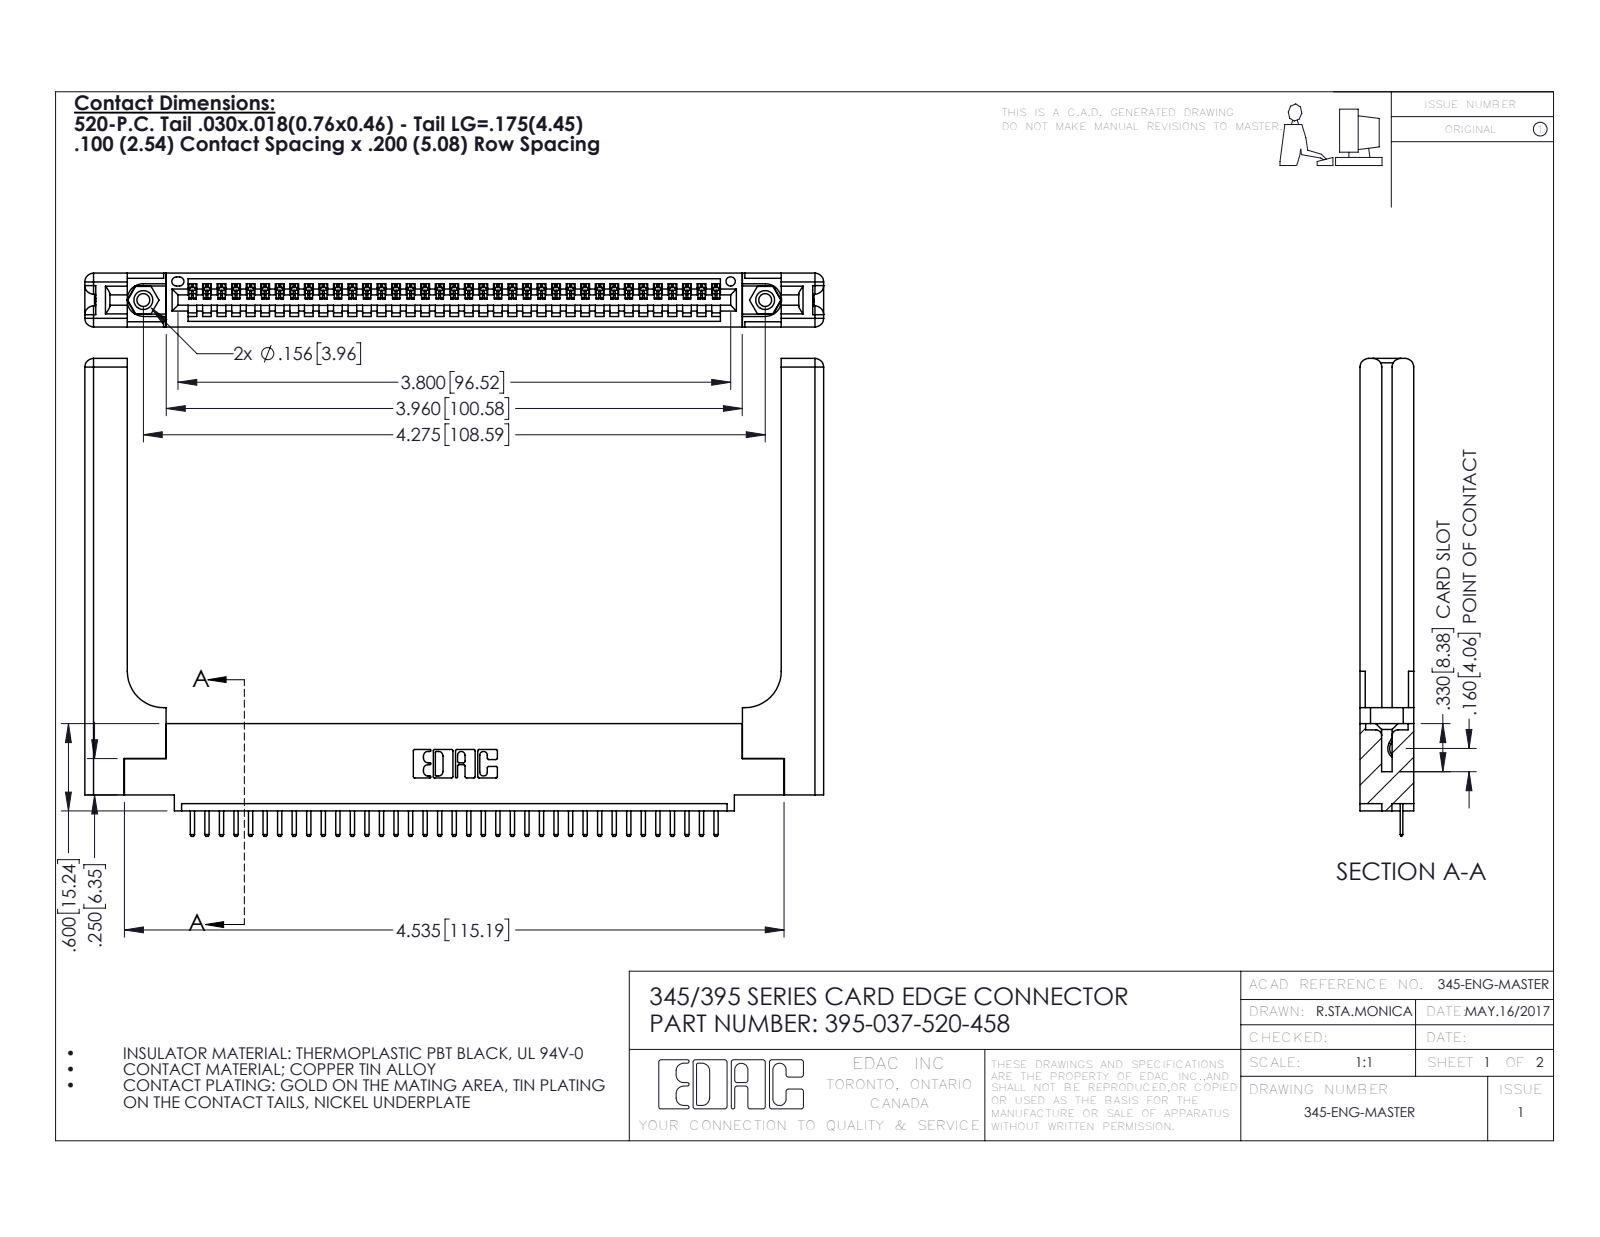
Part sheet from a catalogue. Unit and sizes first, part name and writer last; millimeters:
Units: millimetres
Overall size (bounding box): 129 × 83.4 × 9.4
Round holes (diameter × count): ⌀2.3 ×2, ⌀3.2 ×2, ⌀4 ×2, ⌀1.6 ×1
Round bosses / shafts (diameter × count): ⌀3.9 ×2
Partial cylindrical surfaces — rounded edges, fillets, slot ends (radius × count): R0.3 ×76, R0.2 ×74, R0.3 ×22, R1.5 ×16, R0.2 ×6, R0.8 ×6, R0.7 ×3, R0.8 ×2
Main face-to-face distances: 9.4, 1.8, 7.6, 2.5, 6.9, 0.6, 5.1, 3.8, 3.8, 5.7
Hole centre spacings: 6.9, 102.6, 108.6
Volume: 20 530 mm³ · Surface area: 20 960 mm²
Bodies: 42 solids, 2680 faces (1786 planar, 834 cylindrical, 60 other)
Part name (STEP PRODUCT): 345 Part_0.110 Offset - 0.156 Dia-TH; 345-220-058_345-220-058; 345-250-001_345-250-001-102; 395-037-520-458 (+1 more)
STEP written by: SolidWorks 2016 (CONFIG_CONTROL_DESIGN)
